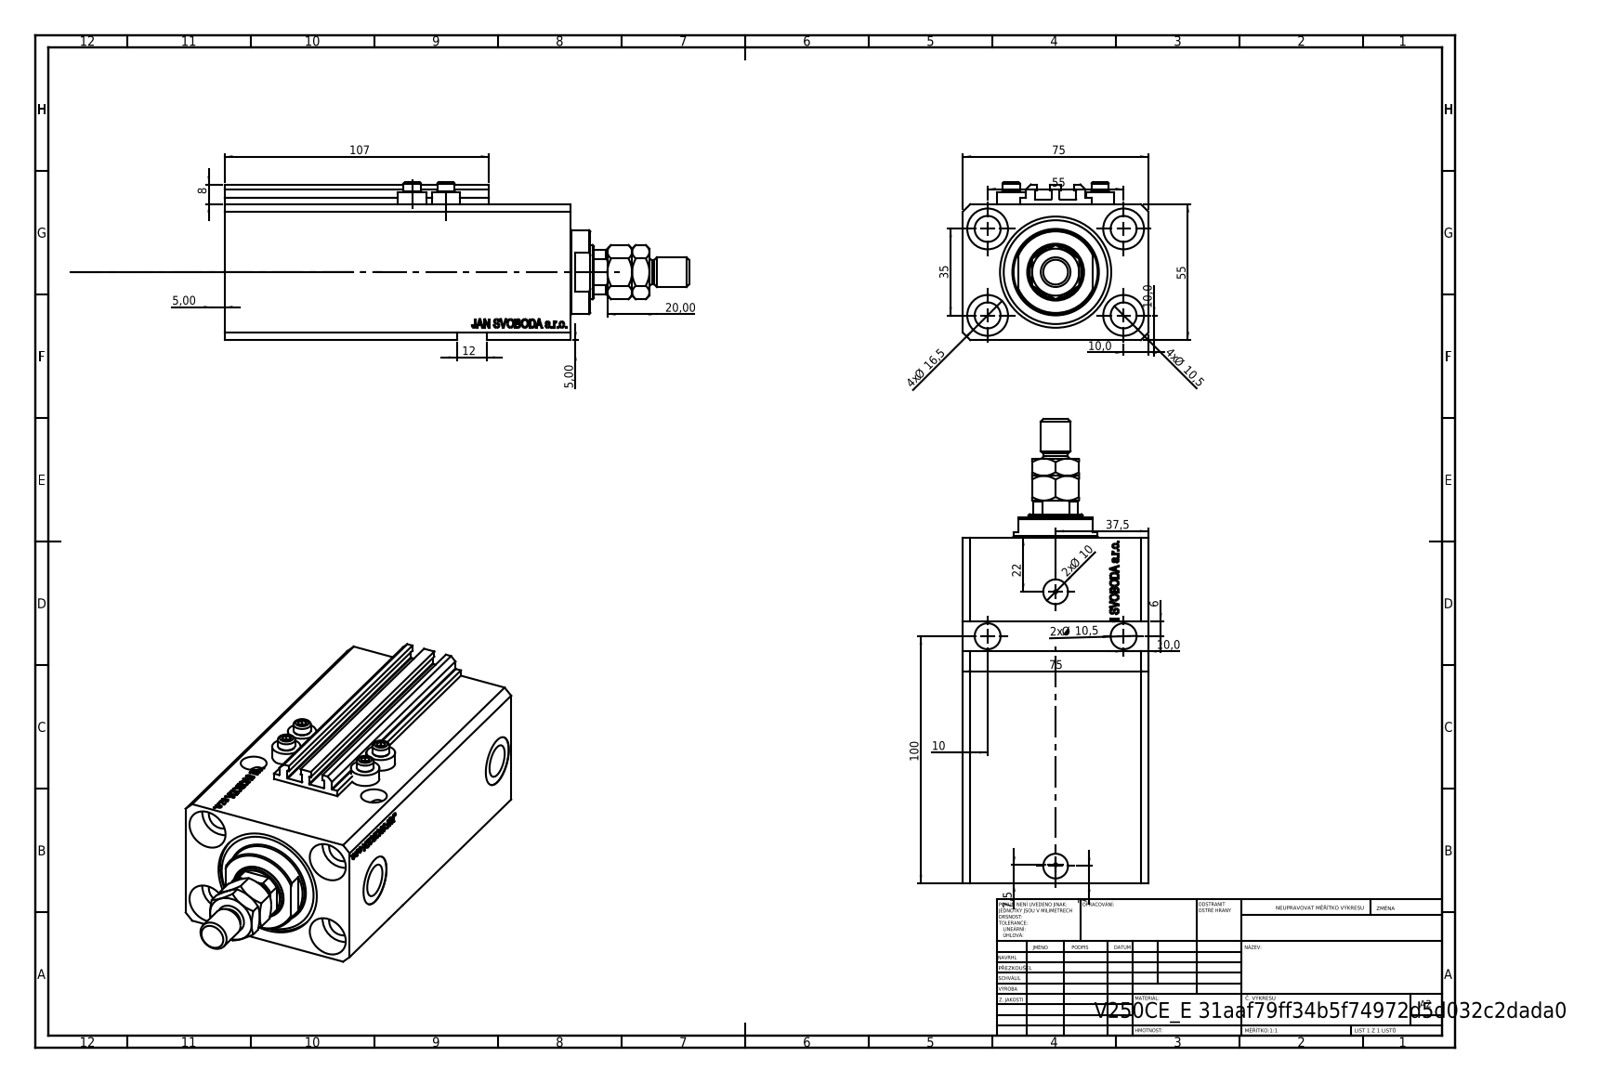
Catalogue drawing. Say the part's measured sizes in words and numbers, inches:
The part is named "MTA; V250CE_C_VCP; V250CE_E_Body; ALLEN BOLT V250CE (+1 more)". Its 3-D file was written by "SolidWorks 2019 (CONFIG_CONTROL_DESIGN)". It is 9 solids with 1113 faces: 529 planar, 130 cylindrical and 454 other. Overall it measures 7.398 by 2.953 by 2.52 inches. Its volume is 30.43 cubic inches and its surface area 184 square inches. Round holes: 7 of diameter 0.413, 4 of diameter 0.049, 4 of diameter 0.157, 4 of diameter 0.65, 2 of diameter 0.394, 2 of diameter 0.518, 2 of diameter 0.787, 1 of diameter 0.866, 1 of diameter 1.26, 1 of diameter 1.772. Round bosses or shafts: 4 of diameter 0.457, 4 of diameter 0.276, 1 of diameter 1.339, 1 of diameter 0.472, 1 of diameter 0.394. Partial cylindrical surfaces (rounded edges, fillets, slot ends): 10 of radius 0.008, 1 of radius 0.413. The main face-to-face distances are 2.165, 2.953, 5.512, 4.445, 1.067, 0.098, 0.39, 0.118, 2.244, 4.055. The hole center spacings are 1.283, 2.165, 0.535, 0.555, 1.016, 1.294, 1.324, 1.378.
